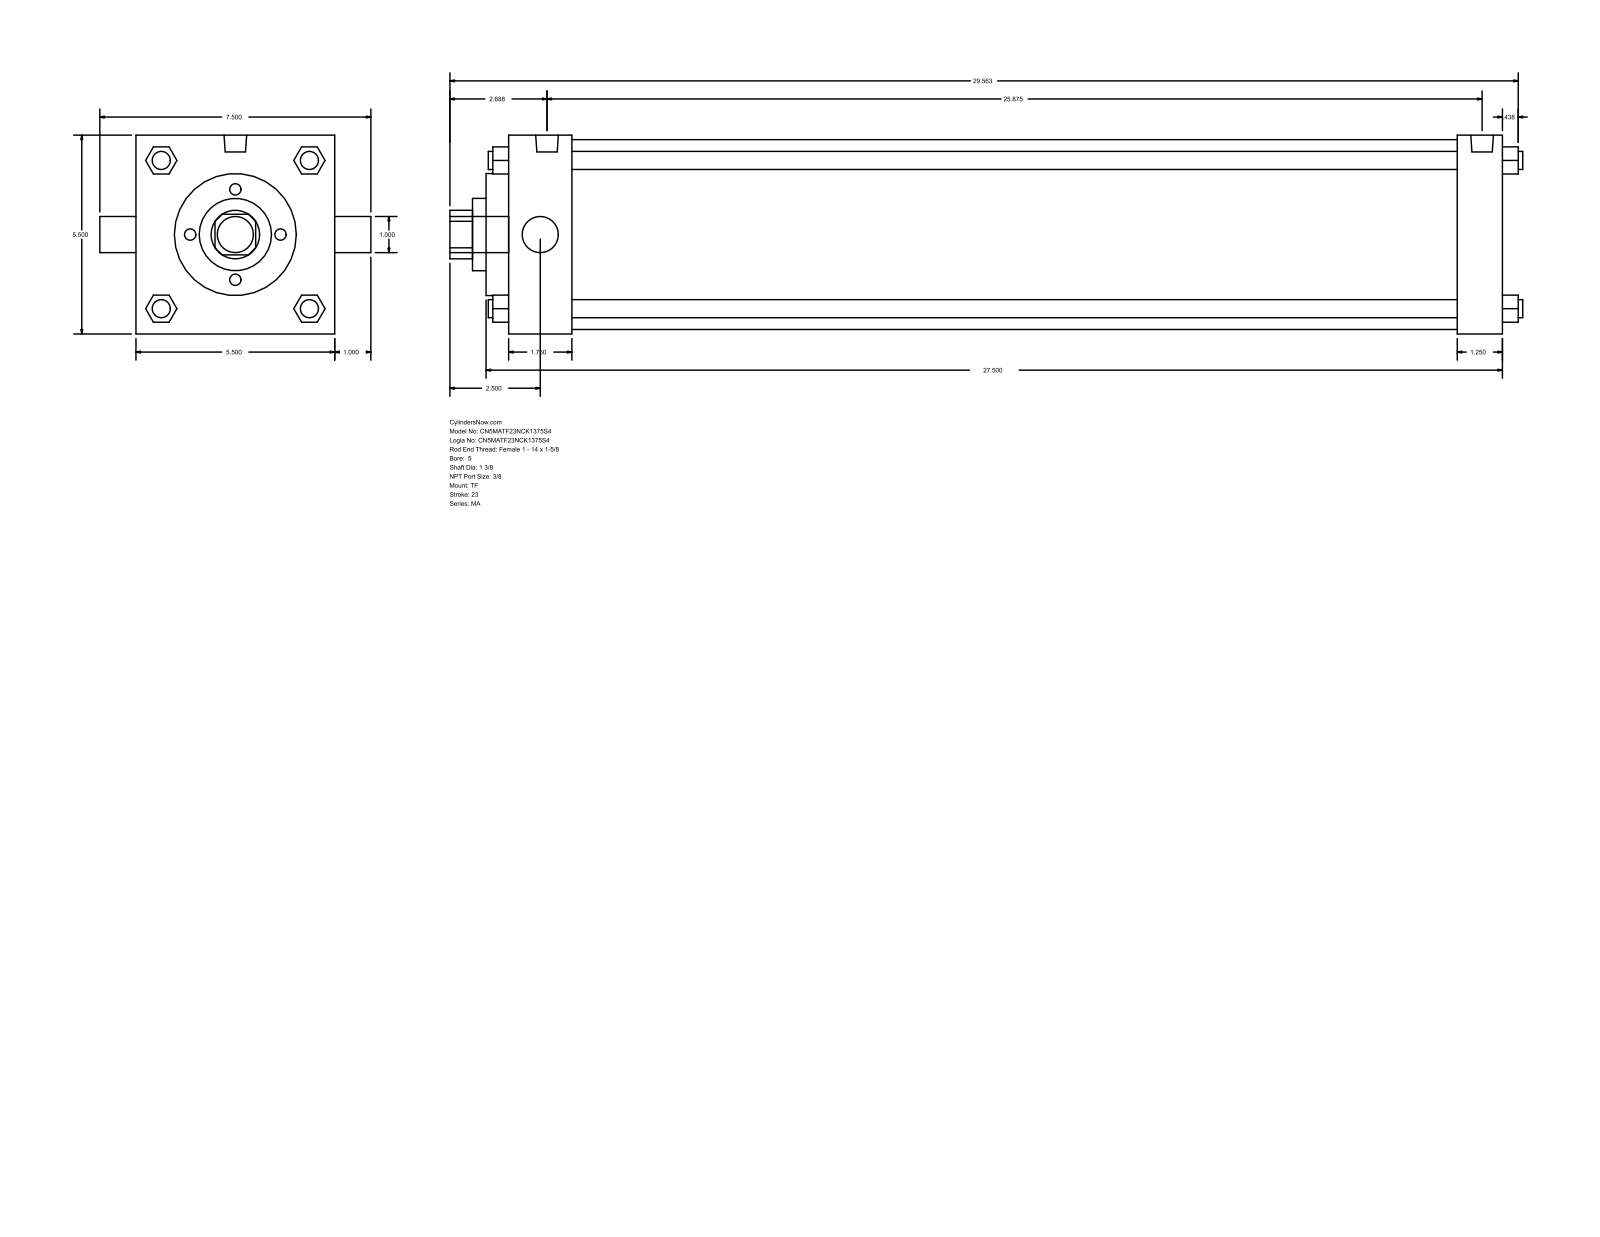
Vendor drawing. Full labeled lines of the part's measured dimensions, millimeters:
Part name (STEP PRODUCT): MA_TF__0500_1.375
STEP written by: GSSL Pune (CONFIG_CONTROL_DESIGN)
Units: millimetres
Bodies: 0 solids, 122 faces (93 planar, 29 cylindrical, 0 other)
Overall size (bounding box): 754.06 × 190.5 × 139.7
Round holes (diameter × count): ⌀25.4 ×1, ⌀34.92 ×1, ⌀50.8 ×1, ⌀85.72 ×1, ⌀133.35 ×1
Round bosses / shafts (diameter × count): ⌀12.7 ×4, ⌀11.11 ×3, ⌀15.93 ×2, ⌀25.4 ×1
Partial cylindrical surfaces — rounded edges, fillets, slot ends (radius × count): R17.06 ×1
Main face-to-face distances: 139.7, 698.5, 666.75, 31.75, 44.45, 622.3, 654.05, 15.87, 60.32, 682.62
